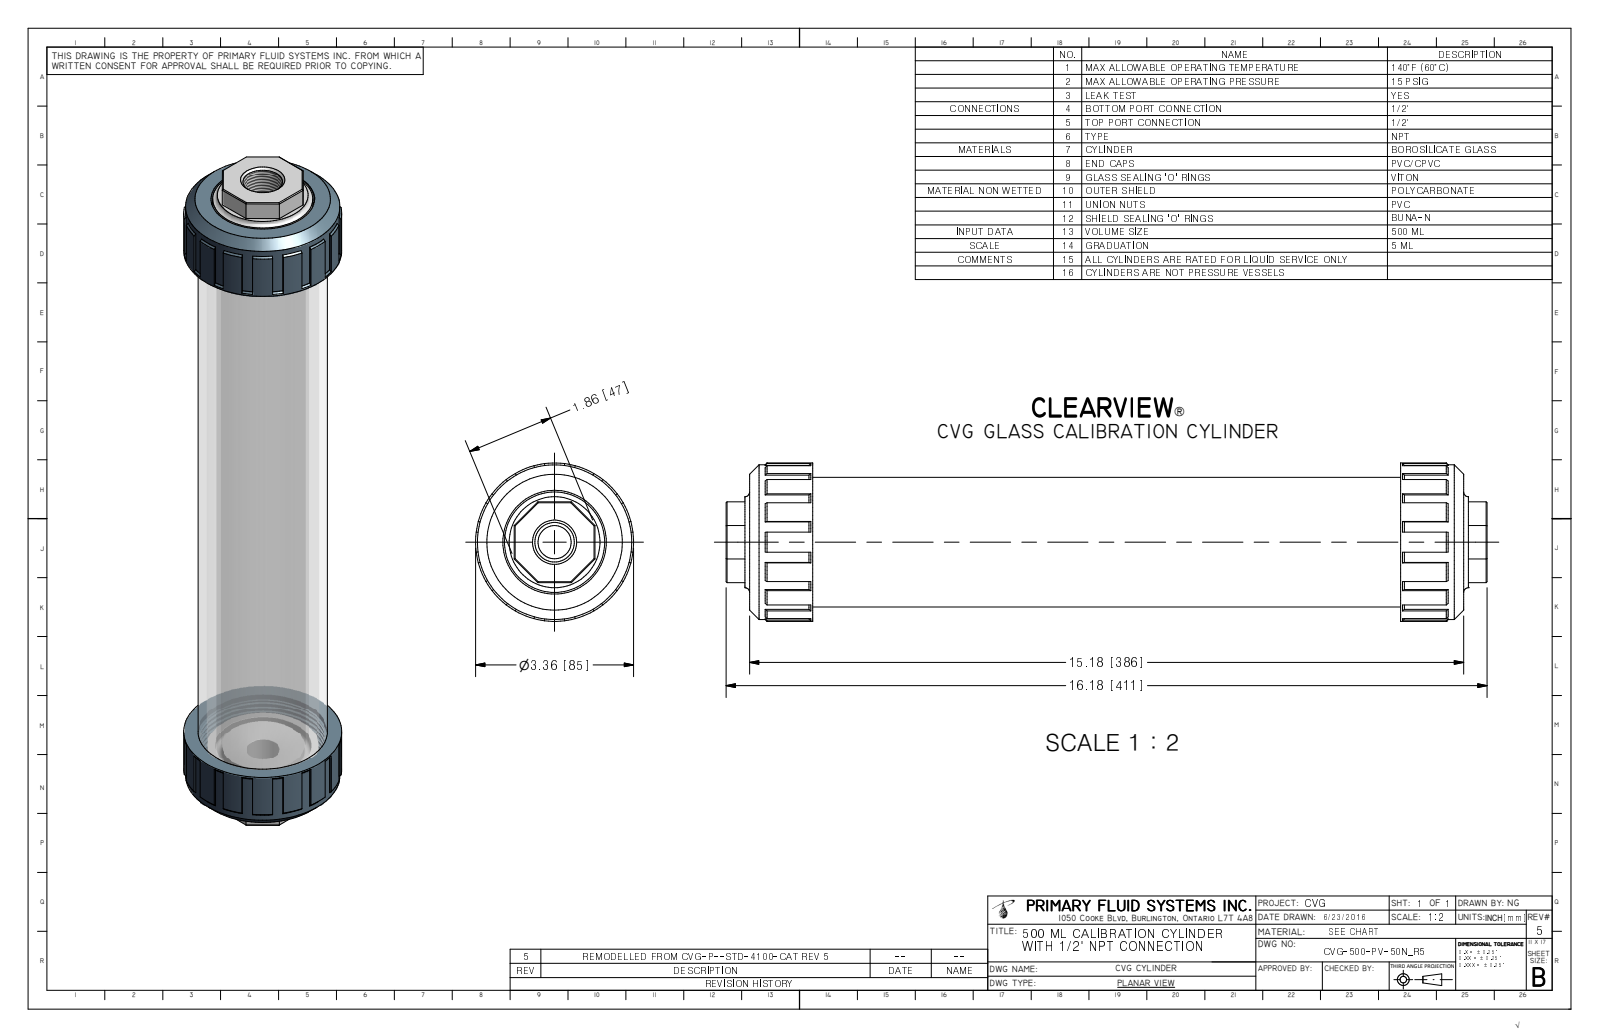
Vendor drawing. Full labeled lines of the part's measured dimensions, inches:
Part name (STEP PRODUCT): CVG-500-PVC-50N_R5; CVG-3-500-POLY-NPT-50_R11; CVG-6-500; CVG-1-500-A_R0 (+1 more)
STEP written by: Autodesk Inventor 2009 (AUTOMOTIVE_DESIGN)
Units: inches
Bodies: 6 solids, 311 faces (84 planar, 33 cylindrical, 194 other)
Overall size (bounding box): 16.18 × 3.36 × 3.36
Volume: 42.83 in³ · Surface area: 522.3 in²
Round holes (diameter × count): ⌀0.704 ×1, ⌀1.811 ×1, ⌀2.05 ×1, ⌀2.4 ×1
Round bosses / shafts (diameter × count): ⌀2.75 ×1, ⌀2.661 ×1, ⌀2.66 ×1, ⌀2.486 ×1, ⌀2.36 ×1, ⌀2.23 ×1, ⌀2.13 ×1, ⌀1.969 ×1
Main face-to-face distances: 0.798, 15.382, 1.715, 1.5, 14.68, 0.702, 13.882, 16.18, 14.584, 1.059
